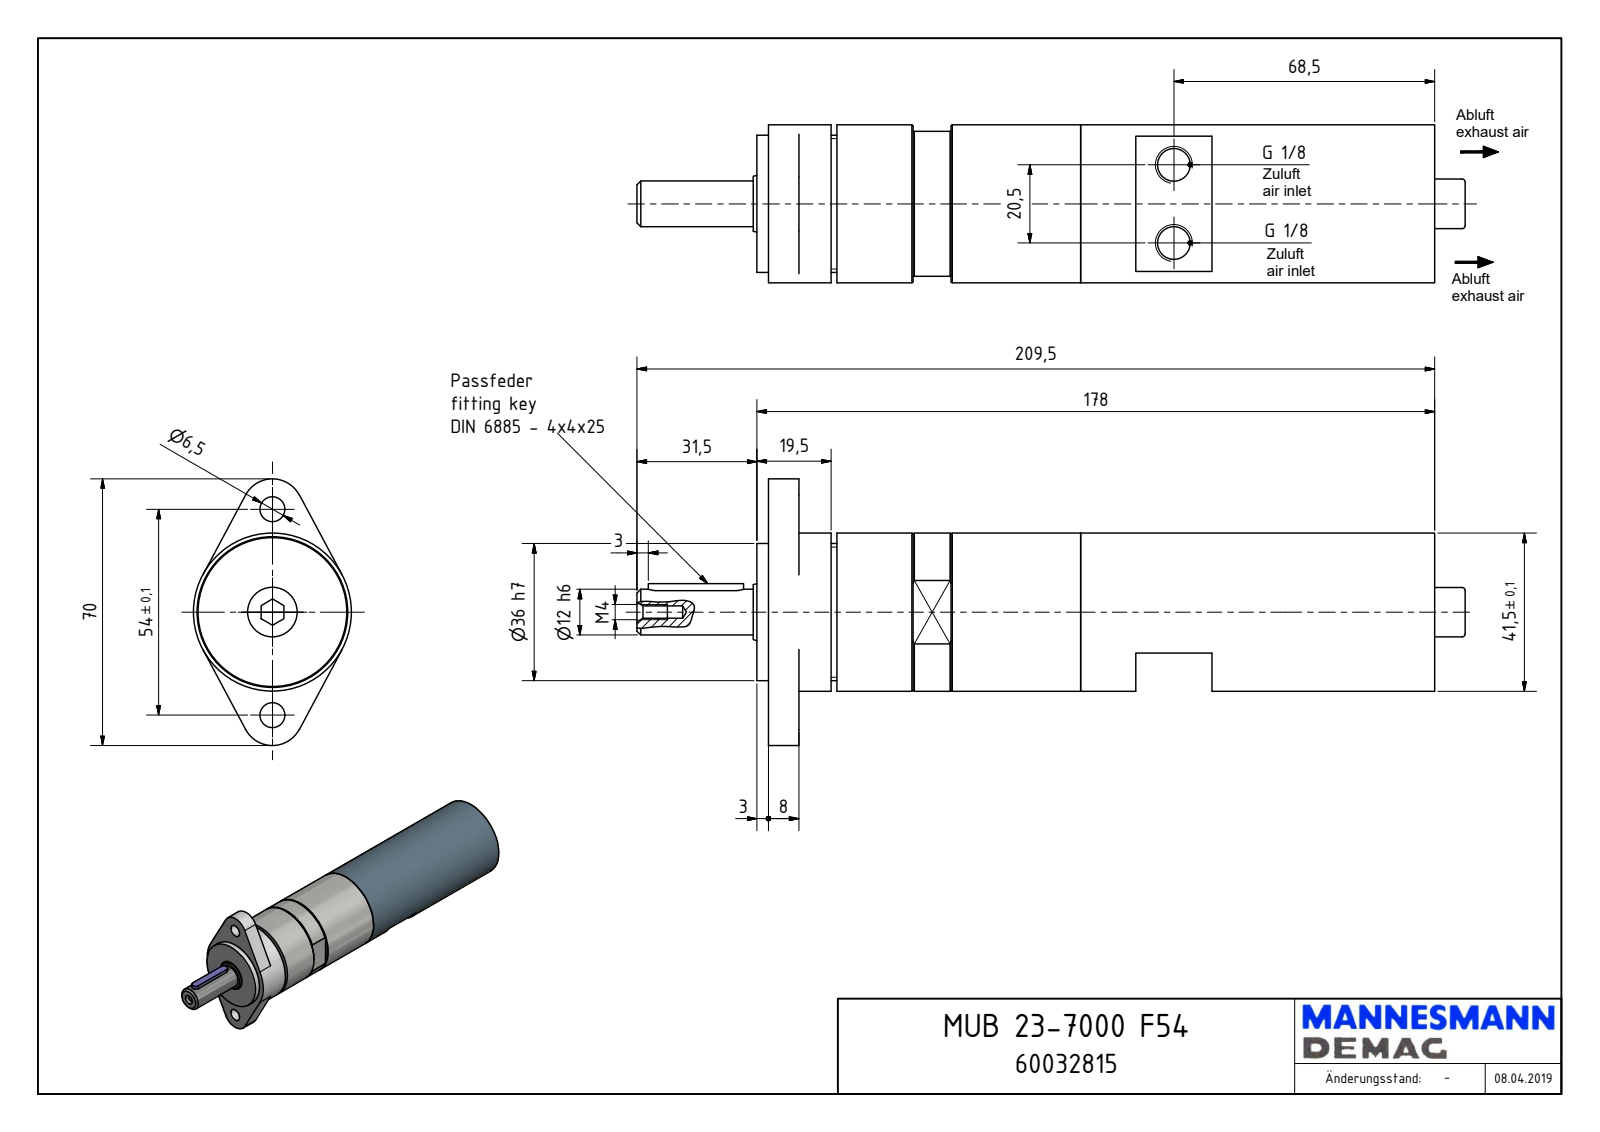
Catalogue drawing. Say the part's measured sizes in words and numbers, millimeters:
The part is named "MUB 23-7000 F54_60032815". Its 3-D file was written by "Autodesk Inventor 2018 (AUTOMOTIVE_DESIGN)". It is 1 solid with 130 faces: 61 planar, 53 cylindrical and 16 other. Overall it measures 217.5 by 70 by 41.5 millimeters. Its volume is 239 653 cubic millimeters and its surface area 36 262 square millimeters. Round holes: 2 of diameter 2, 2 of diameter 6.5, 2 of diameter 8.57, 1 of diameter 3.24, 1 of diameter 8.5, 1 of diameter 13, 1 of diameter 16, 1 of diameter 38, 1 of diameter 39.5. Round bosses or shafts: 1 of diameter 41.5, 1 of diameter 39, 1 of diameter 36, 1 of diameter 14.95, 1 of diameter 12, 1 of diameter 8. Partial cylindrical surfaces (rounded edges, fillets, slot ends): 4 of radius 2, 2 of radius 1.6, 2 of radius 2.5, 2 of radius 8, 1 of radius 8.1, 1 of radius 11.83. The main face-to-face distances are 5, 0.37, 5.37, 175, 169.63, 170, 3, 172.63, 173, 178. The hole center spacings are 12.94, 26.75, 27, 32.82, 20.5, 25, 54.
